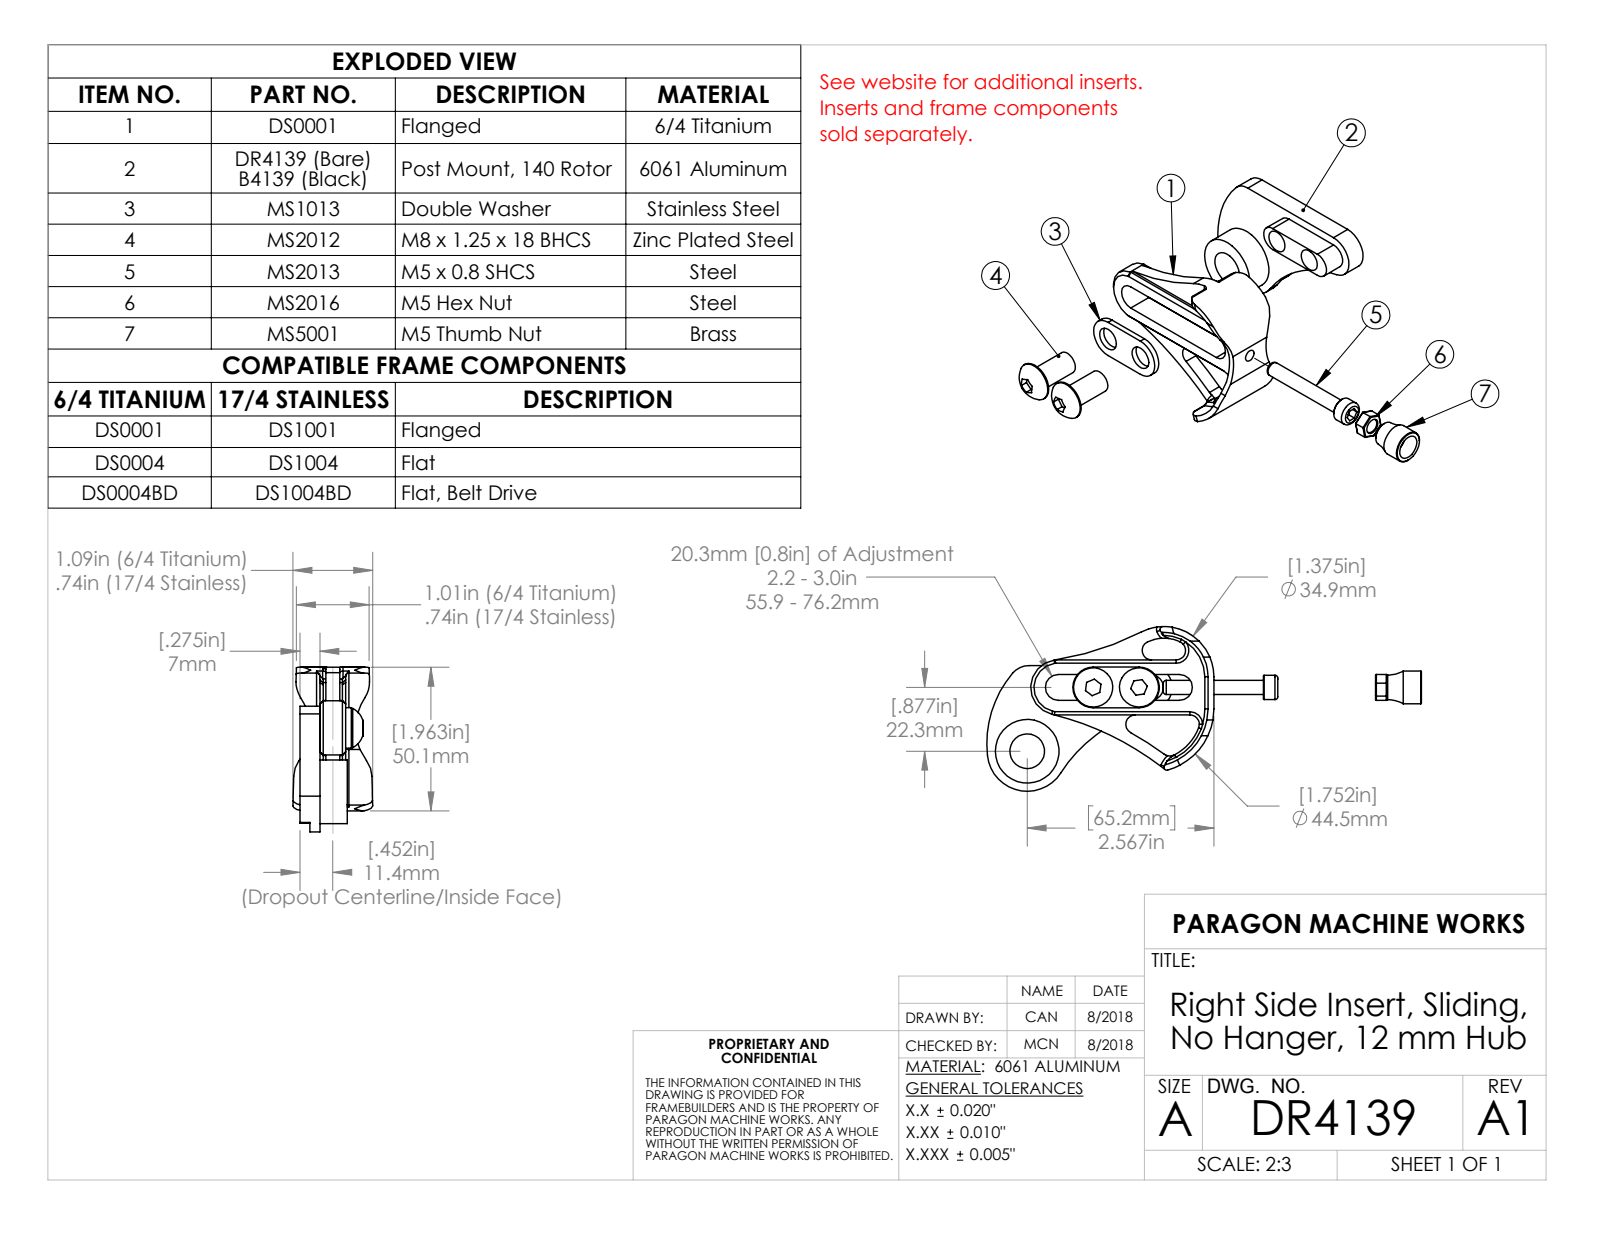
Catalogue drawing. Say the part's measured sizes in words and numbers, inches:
The part is named "DR4139_Flanged; MS2016; MS5001; MS2013 (+4 more)". Its 3-D file was written by "SolidWorks 2018 (AUTOMOTIVE_DESIGN)". It is 8 solids with 258 faces: 77 planar, 112 cylindrical and 69 other. Overall it measures 4.002 by 2.263 by 1.097 inches. Its volume is 1.837 cubic inches and its surface area 29.23 square inches. Round holes: 2 of diameter 0.312, 2 of diameter 0.327, 1 of diameter 0.166, 1 of diameter 0.197, 1 of diameter 0.335, 1 of diameter 0.477. Round bosses or shafts: 2 of diameter 0.539, 2 of diameter 0.315, 1 of diameter 0.875, 1 of diameter 0.449. Partial cylindrical surfaces (rounded edges, fillets, slot ends): 12 of radius 0.01, 4 of radius 0.13, 4 of radius 0.178, 4 of radius 0.375, 3 of radius 0.3, 2 of radius 0.039, 2 of radius 0.04, 2 of radius 0.045. The main face-to-face distances are 0.275, 0.629, 0.354, 0.081, 0.273, 0.356, 0.079, 0.708, 0.433, 0.512. The hole center spacings are 0.63, 1.262, 1.77.
